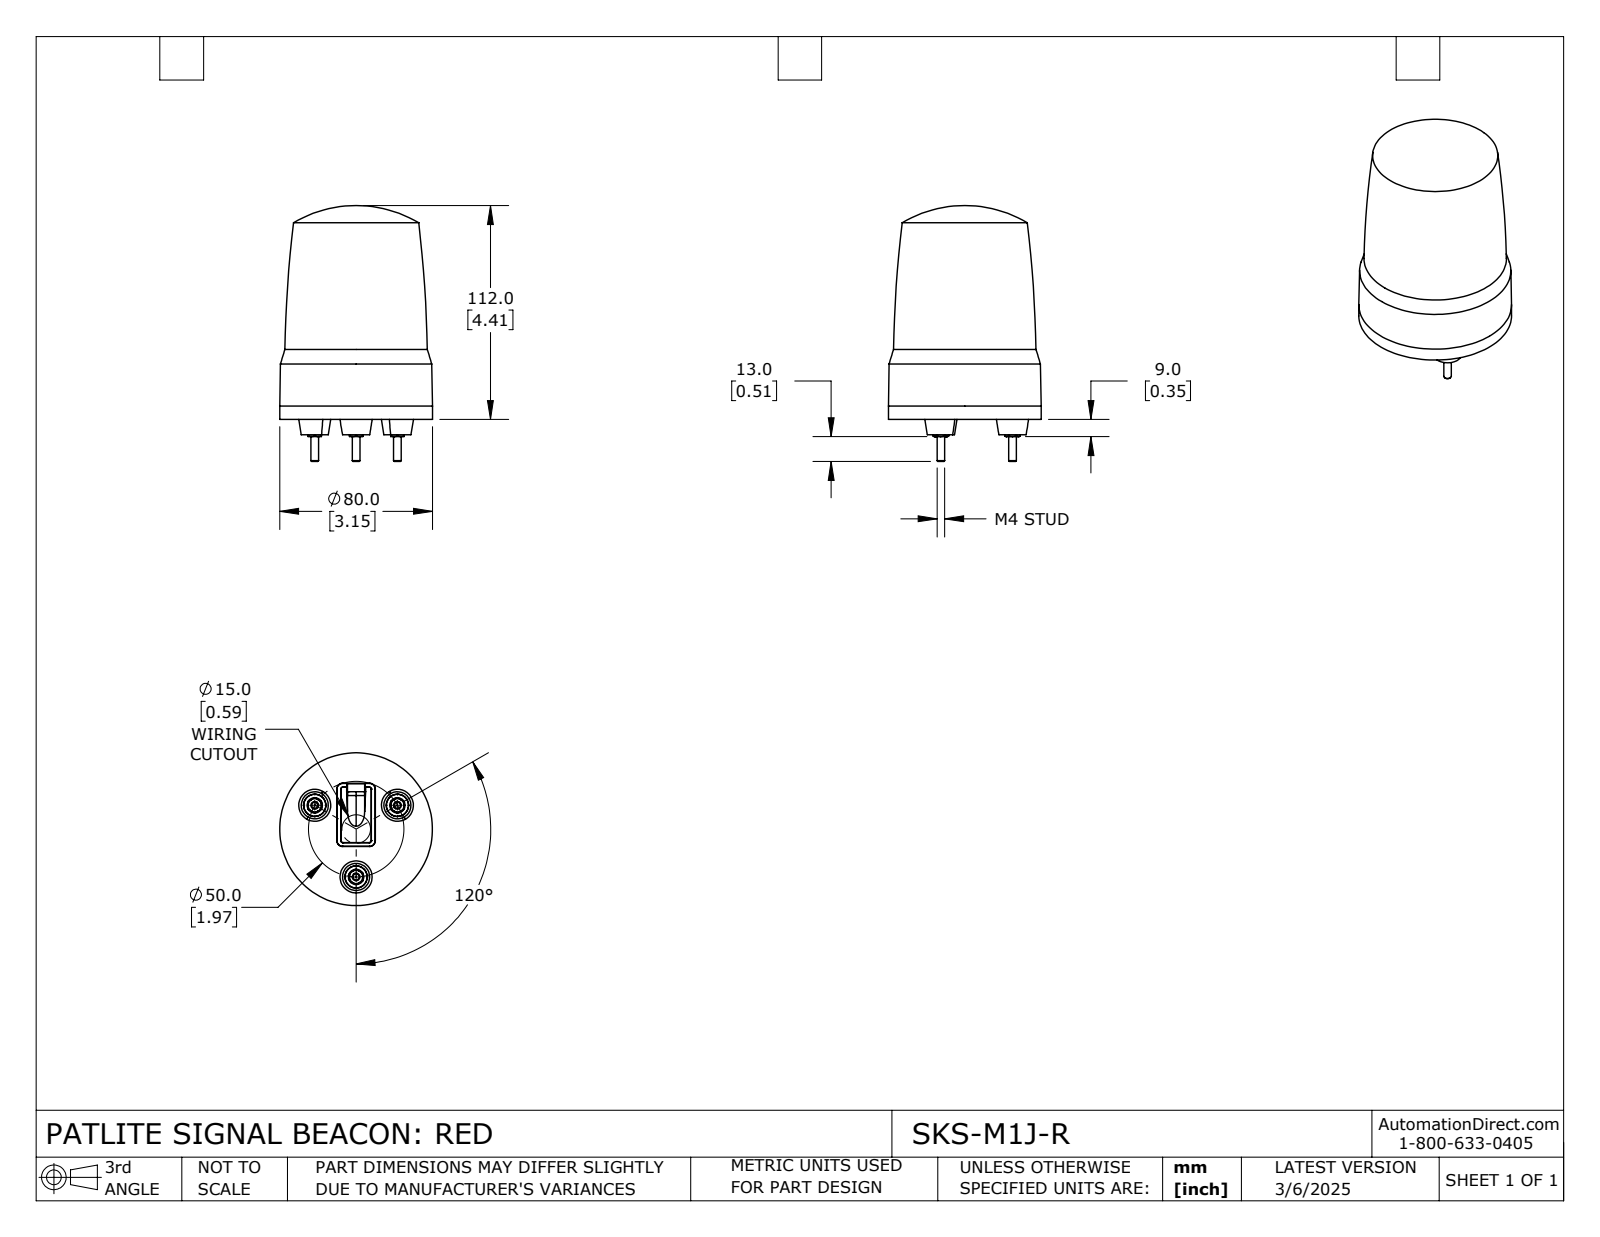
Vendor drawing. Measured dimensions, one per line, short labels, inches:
name: SKS-M1J-R
written by: SolidWorks 2024 (CONFIG_CONTROL_DESIGN)
unit: in
bodies: 1 solid, 138 faces (47 planar, 14 cylindrical, 77 other)
size: 5.276 × 3.15 × 3.15
volume: 28.27 in³; area: 54.88 in²
bosses: 3× ⌀0.315, 3× ⌀0.157, 1× ⌀3.15
face distances: 0.033, 0.096, 0.063, 0.209, 0.242, 0.305, 0.106, 0.315, 0.348, 0.411
